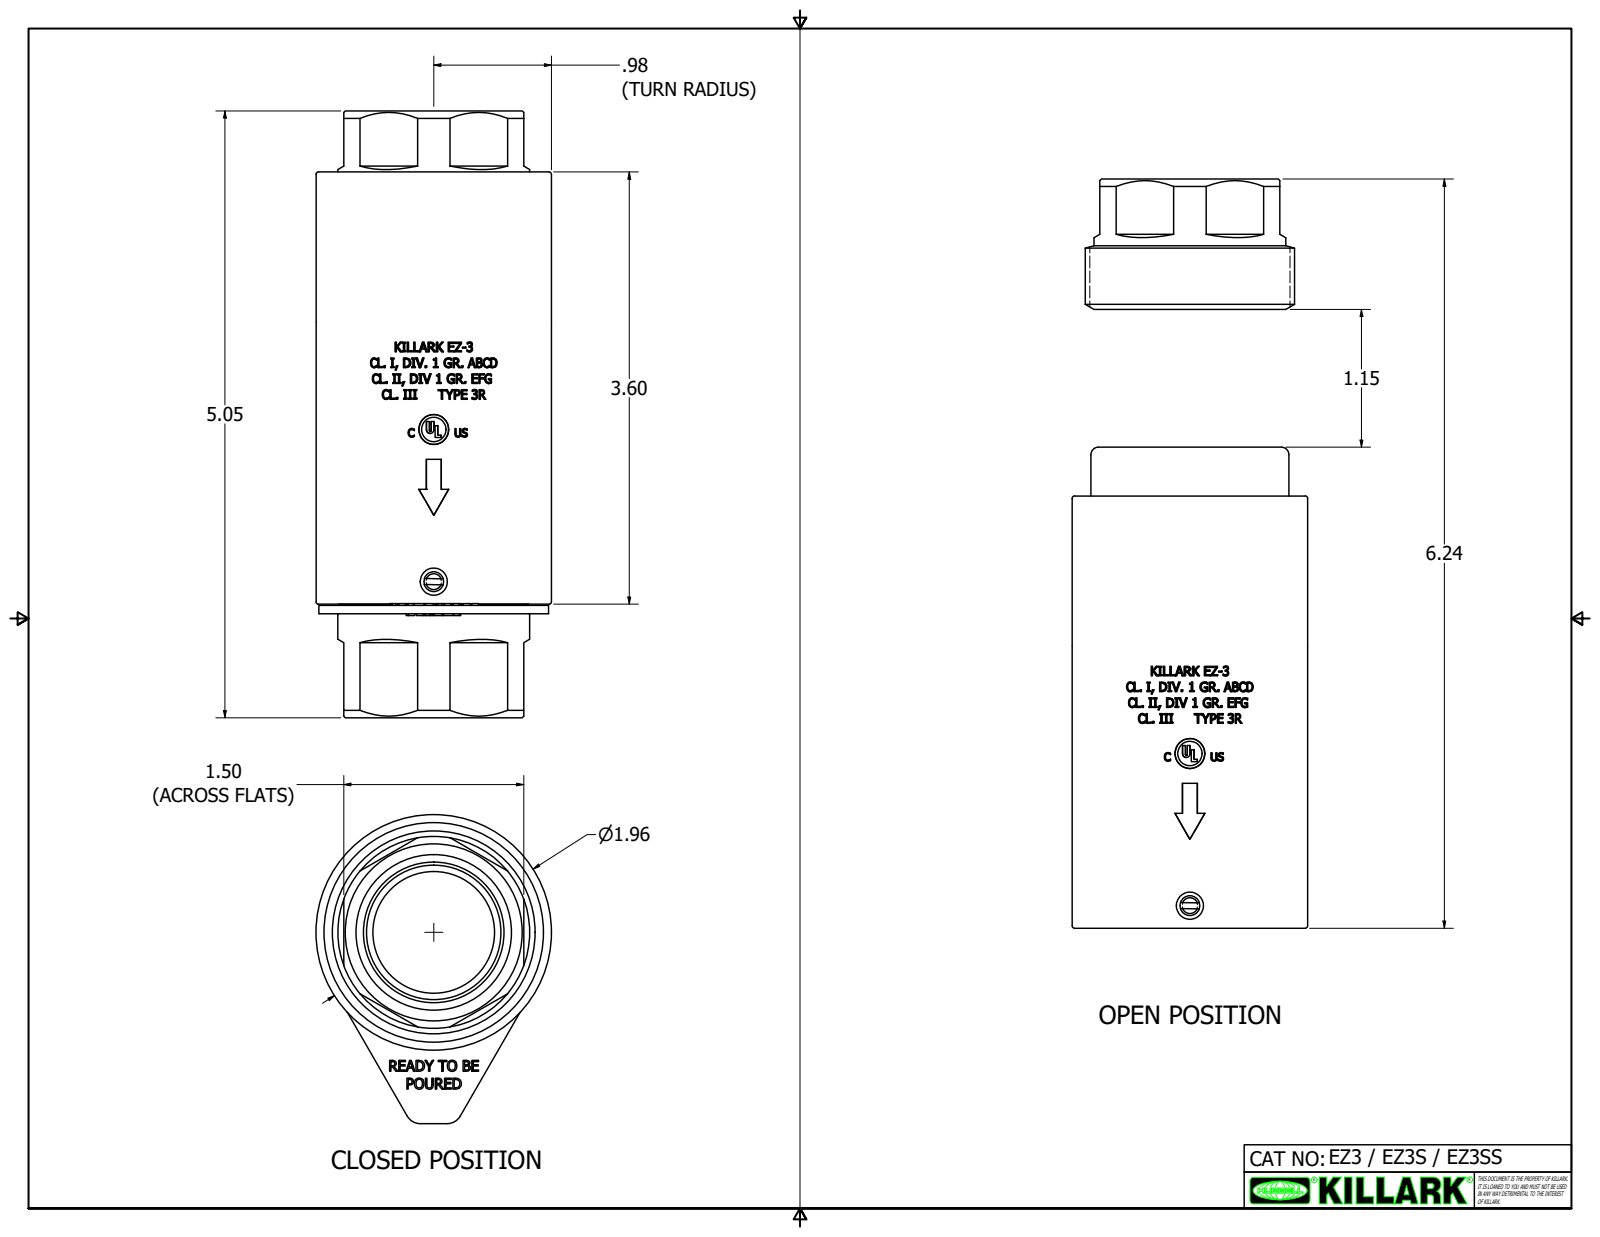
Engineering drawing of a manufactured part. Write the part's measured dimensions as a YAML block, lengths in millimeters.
part_name: "51993-1_Shrinkwrap_1"
step_written_by: "Autodesk Inventor 2020 (AUTOMOTIVE_DESIGN)"
units: millimeters
bodies: {solids: 5, faces: 1357, planar: 733, cylindrical: 116, other: 508}
overall_size: [128.4, 65.4, 49.8]
volume: 103600
surface_area: 56990
round_holes:
  - {diameter: 4.2, count: 1}
  - {diameter: 25.7, count: 1}
  - {diameter: 34.9, count: 1}
  - {diameter: 37.1, count: 1}
  - {diameter: 37.8, count: 1}
  - {diameter: 39.3, count: 1}
  - {diameter: 41.9, count: 1}
  - {diameter: 42.9, count: 1}
  - {diameter: 43, count: 1}
  - {diameter: 44.4, count: 1}
round_bosses_or_shafts:
  - {diameter: 49.8, count: 1}
  - {diameter: 44.3, count: 1}
  - {diameter: 41.9, count: 1}
  - {diameter: 40.6, count: 1}
  - {diameter: 39, count: 1}
  - {diameter: 38.2, count: 1}
partial_cylinders:
  - {radius: 2.5, count: 2}
  - {radius: 3.2, count: 2}
  - {radius: 3.6, count: 2}
  - {radius: 20, count: 1}
  - {radius: 21.1, count: 1}
  - {radius: 24.3, count: 1}
  - {radius: 24.7, count: 1}
face_to_face_distances: [38.1, 1.8, 77, 78.8, 2, 76.8, 106.4, 19.8, 27.6, 104.3]
